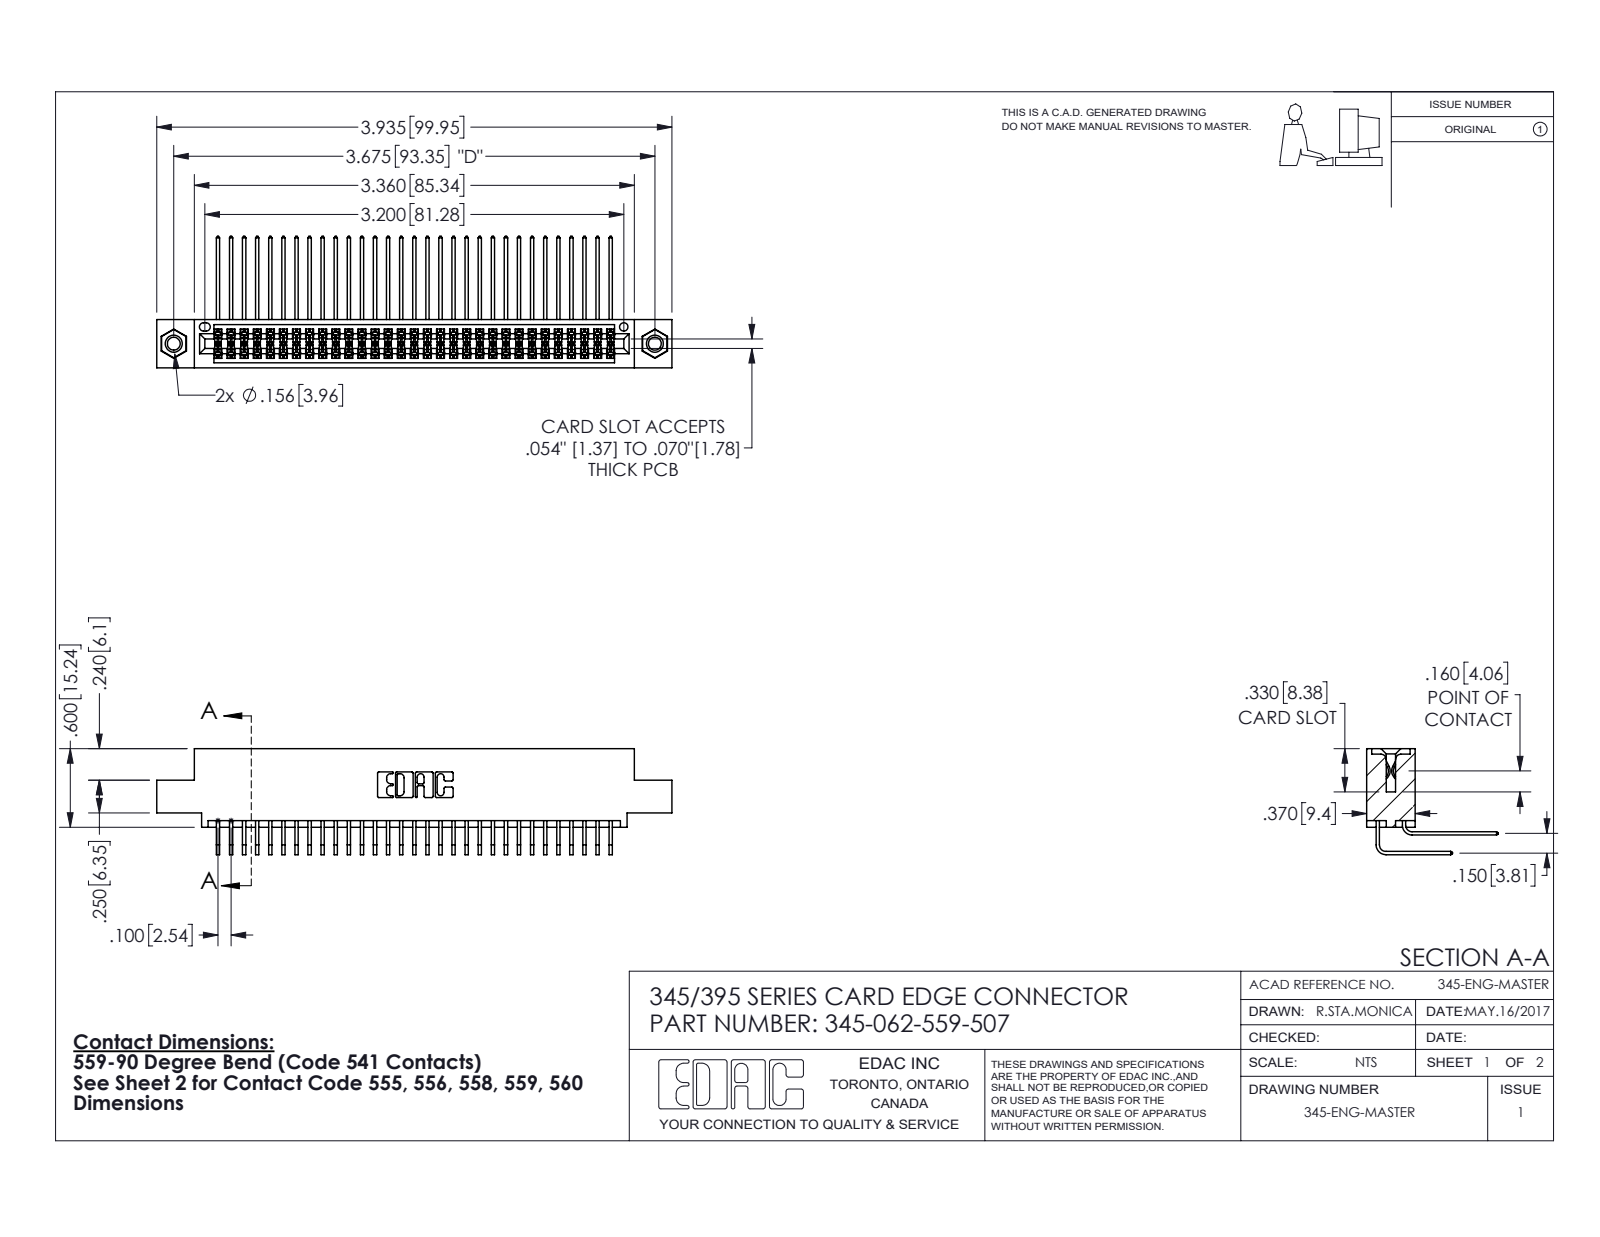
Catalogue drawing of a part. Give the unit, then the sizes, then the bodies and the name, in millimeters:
Units: millimetres
Overall size (bounding box): 99.9 × 25.5 × 20.5
Round holes (diameter × count): ⌀2.5 ×2, ⌀3.2 ×2, ⌀4 ×2, ⌀1.6 ×1
Round bosses / shafts (diameter × count): ⌀3.9 ×2
Partial cylindrical surfaces — rounded edges, fillets, slot ends (radius × count): R0.2 ×124, R0.3 ×22, R0.2 ×6, R0.8 ×6, R0.7 ×3, R0.4 ×2, R0.5 ×2, R0.6 ×2
Main face-to-face distances: 1.8, 7.6, 5.1, 9.4, 2.5, 6.9, 0.6, 5.7, 3.8, 4.4
Hole centre spacings: 6.9, 87.4, 93.3
Volume: 9 880 mm³ · Surface area: 16 190 mm²
Bodies: 65 solids, 3414 faces (2286 planar, 1112 cylindrical, 16 other)
Part name (STEP PRODUCT): 345-292-001_559 Tail - 2; 345-250-001_345-250-005-103; 345-062-559-507; 345 Part_0.110 Offset - 0.156 Dia-TI (+1 more)
STEP written by: SolidWorks 2016 (CONFIG_CONTROL_DESIGN)
